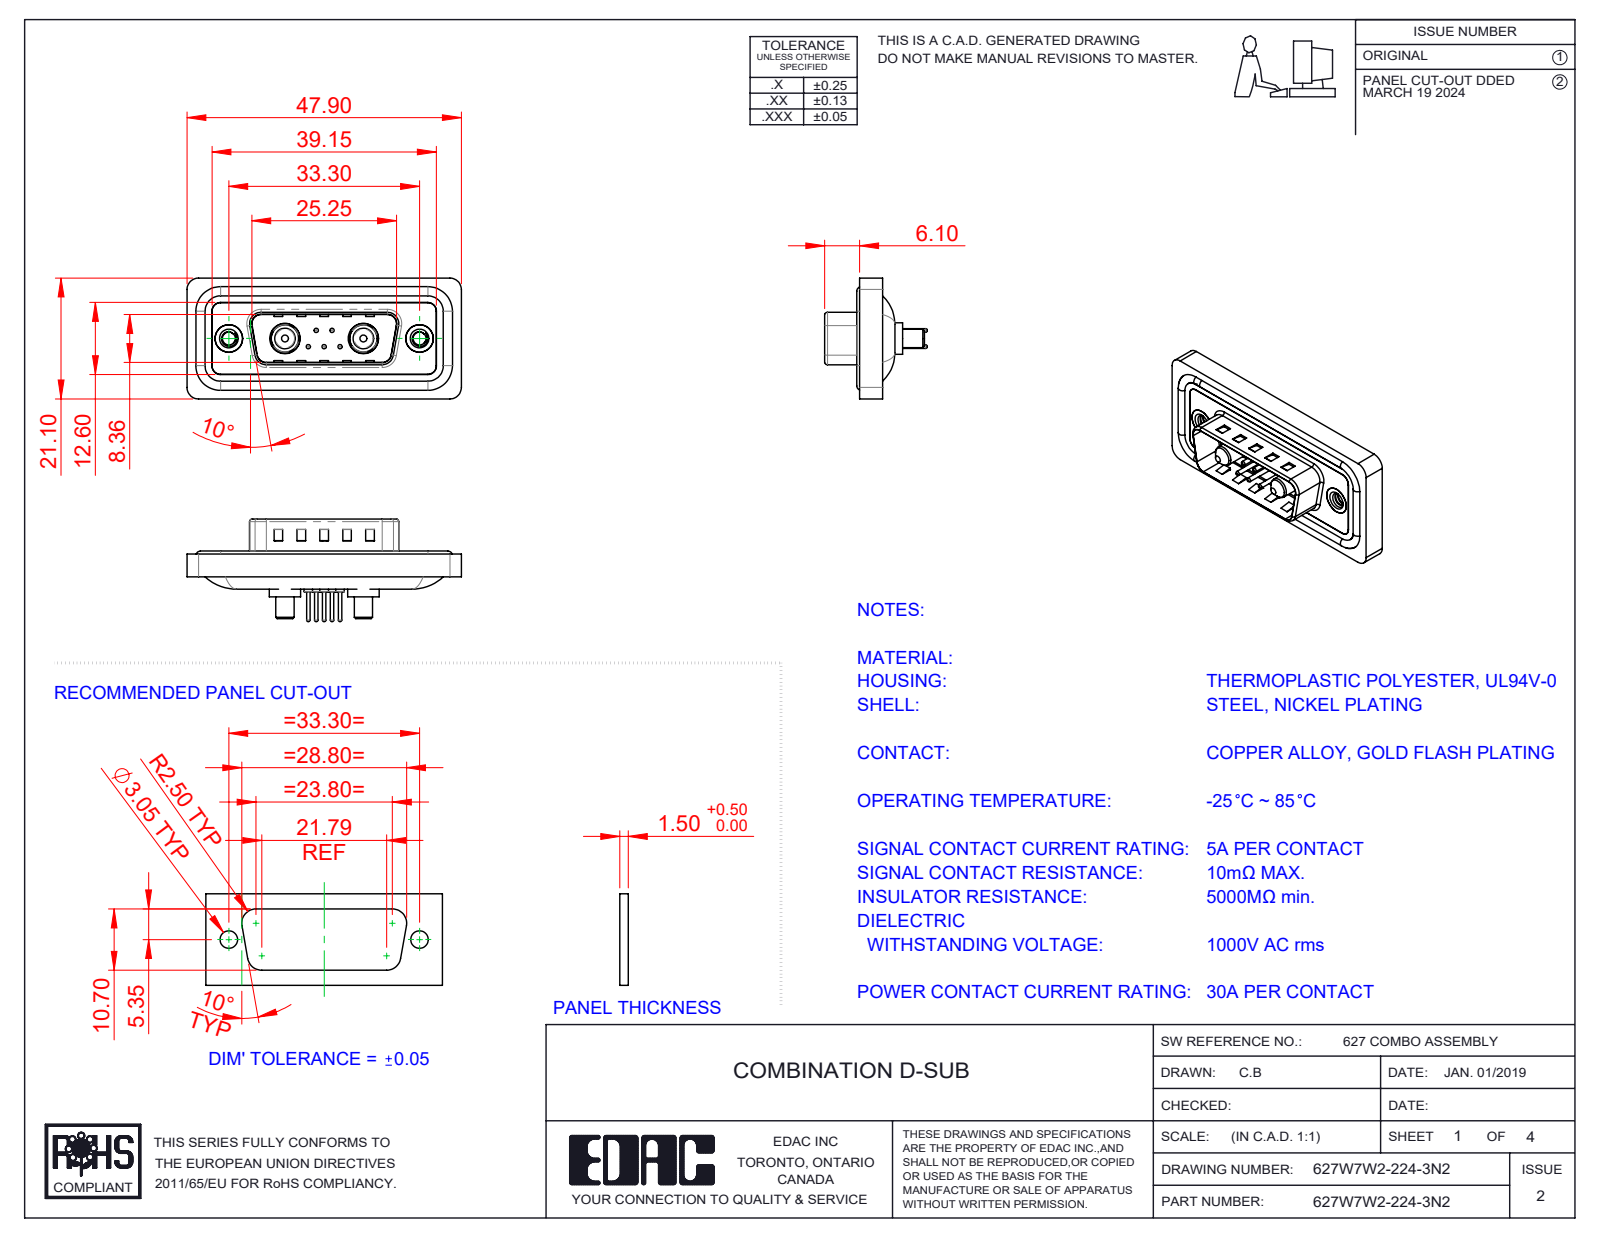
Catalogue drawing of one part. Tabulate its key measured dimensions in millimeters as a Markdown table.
| quantity | value |
| --- | --- |
| part name | 627Combo Shell Rear_15 Contacts; 627Combo Shell Front_15 Contacts; 627Combo Waterproof Housing_15 Contacts; Power Pin_30A S (+5 more) |
| STEP written by | SolidWorks 2023 (CONFIG_CONTROL_DESIGN) |
| units | millimeters |
| bodies | 16 solids, 710 faces (232 planar, 292 cylindrical, 186 other) |
| overall size | 47.9 × 21.1 × 17.9 |
| volume | 5 531 mm³ |
| surface area | 8 802 mm² |
| round holes (diameter × count) | 0.75 × 5, 1.6 × 5, 2 × 5, 2.26 × 2, 4 × 2, 4.8 × 2, 4.85 × 2, 5 × 2, 5.3 × 2 |
| round bosses / shafts (diameter × count) | 1.5 × 5, 0.6 × 5, 1.6 × 4, 5.5 × 2, 5.2 × 2, 4.9 × 2, 4.75 × 2, 3.75 × 2 |
| partial cylindrical surfaces (radius × count) | 1.5 × 26, 2 × 20, 0.5 × 8, 1.6 × 8, 0.25 × 4, 0.6 × 4, 0.65 × 4, 0.9 × 4 |
| main face-to-face distances | 0.4, 1.1, 1.5, 1.6, 0.5, 3.1, 2.9, 0.82, 9.58, 2.5 |
| hole center spacings | 3.16, 2.77, 9.8, 23.5, 4.31, 4.33, 5.03, 5.04 |
